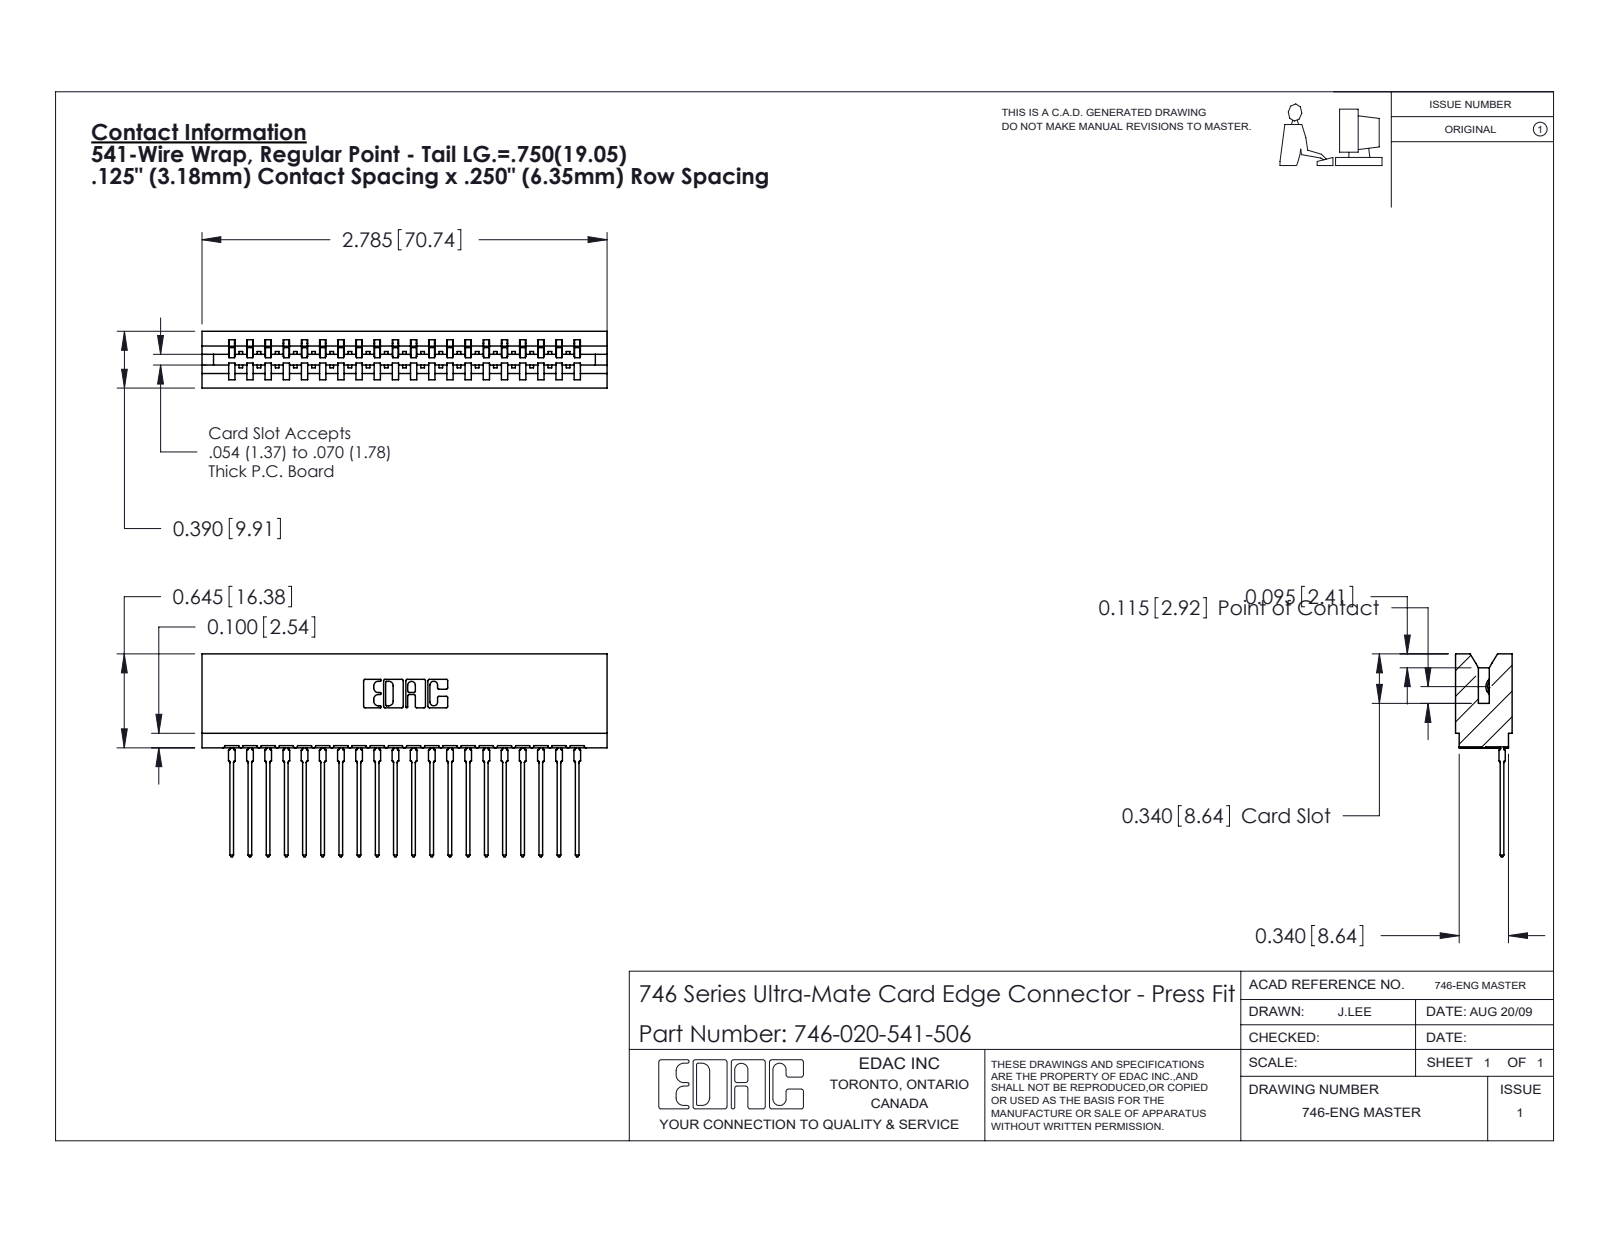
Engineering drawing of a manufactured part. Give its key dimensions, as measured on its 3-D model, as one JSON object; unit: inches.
{"part_name": "746-292-001_541; 746 Part_.340 Slot Depth - 06; 746-020-541-506", "step_written_by": "SolidWorks 2020 (CONFIG_CONTROL_DESIGN)", "units": "inches", "bodies": {"solids": 21, "faces": 2258, "planar": 1316, "cylindrical": 422, "other": 520}, "overall_size": [2.785, 1.394, 0.39], "volume_in3": 0.497, "surface_area_in2": 17.29, "partial_cylinders_radius": [[0.021, 40], [0.01, 22], [0.015, 21], [0.007, 6], [0.031, 6], [0.005, 4], [0.011, 4], [0.026, 3]], "face_to_face_distances": [0.25, 0.057, 0.333, 0.39, 0.5, 0.025, 0.307, 0.125, 0.042, 0.125]}
